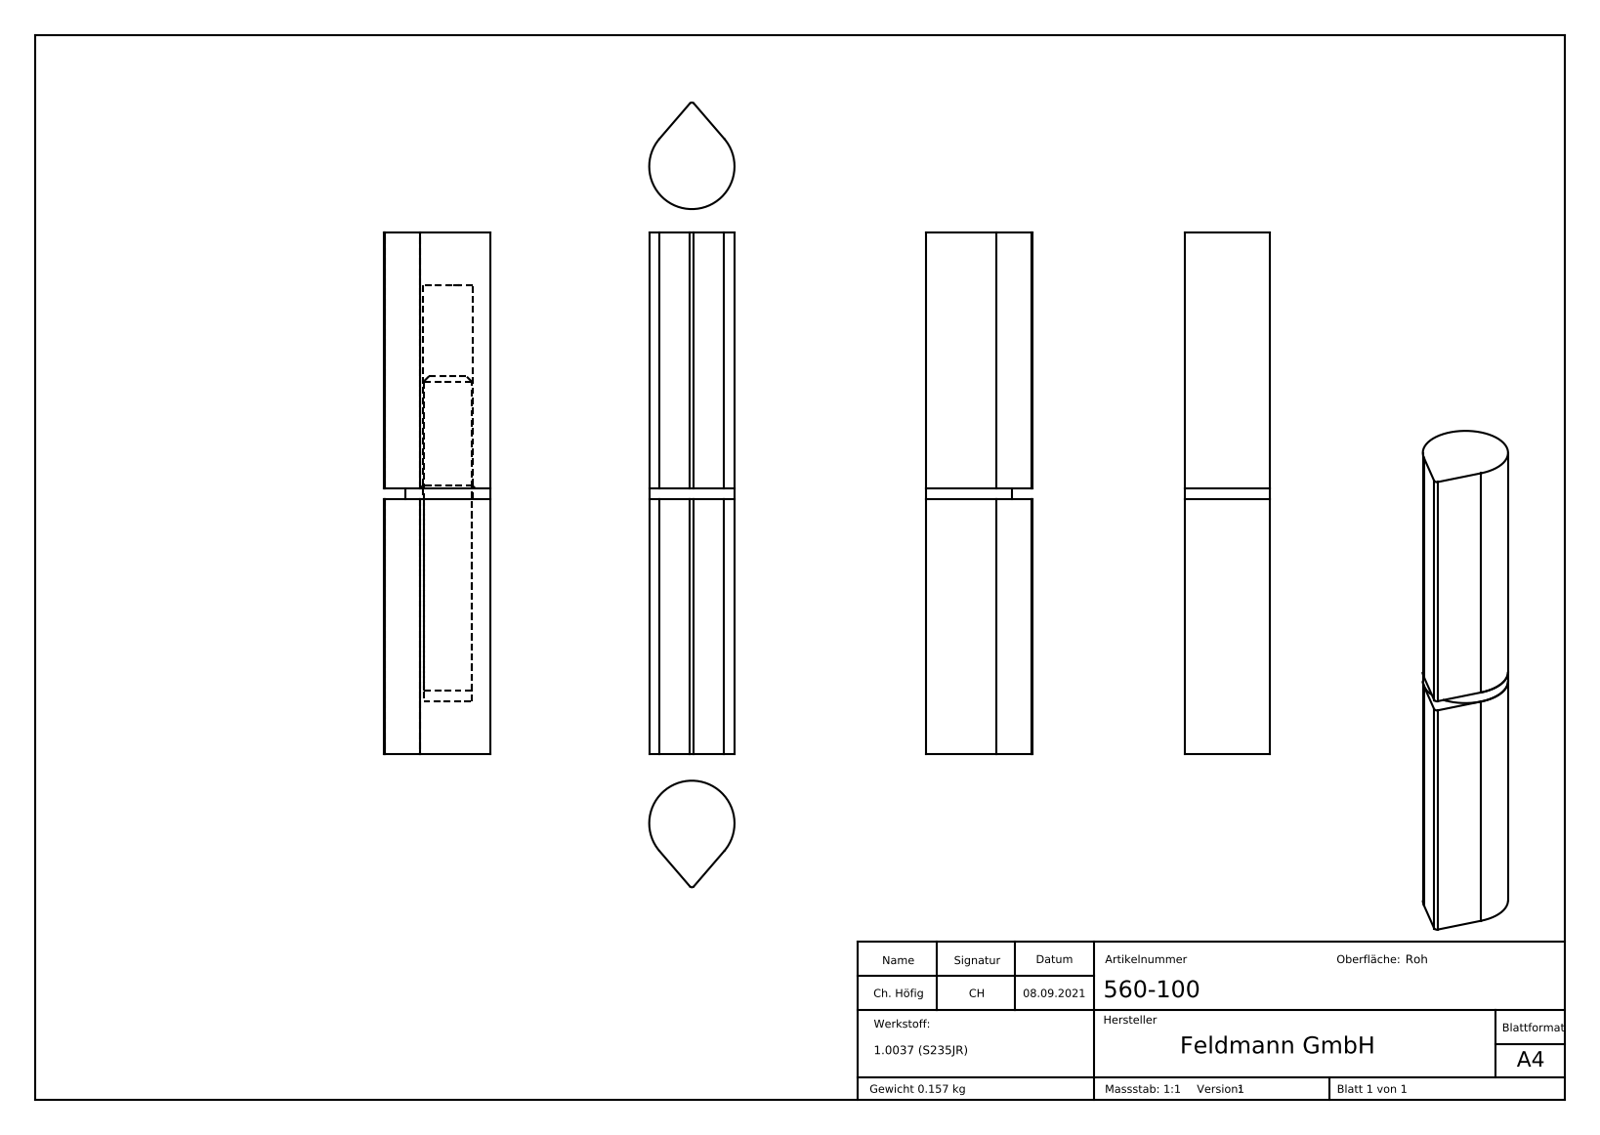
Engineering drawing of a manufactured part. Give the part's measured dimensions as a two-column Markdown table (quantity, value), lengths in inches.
| quantity | value |
| --- | --- |
| part name | 560-xx Teil3; 560-xx Teil2; 560-xx Teil1; 560-xx Teil3_560-100 Teil3 (+3 more) |
| STEP written by | SolidWorks 2018 (CONFIG_CONTROL_DESIGN) |
| units | inches |
| bodies | 4 solids, 255 faces (132 planar, 9 cylindrical, 114 other) |
| overall size | 3.858 × 0.787 × 0.63 |
| volume | 1.228 in³ |
| surface area | 16.32 in² |
| round holes (diameter × count) | 0.358 × 1, 0.364 × 1, 0.37 × 1 |
| round bosses / shafts (diameter × count) | 0.63 × 1, 0.354 × 1 |
| partial cylindrical surfaces (radius × count) | 0.02 × 1 |
| main face-to-face distances | 1.89, 1.969, 0.079, 3.858, 1.496, 0.394, 3.465, 1.575, 3.071, 0.472 |
